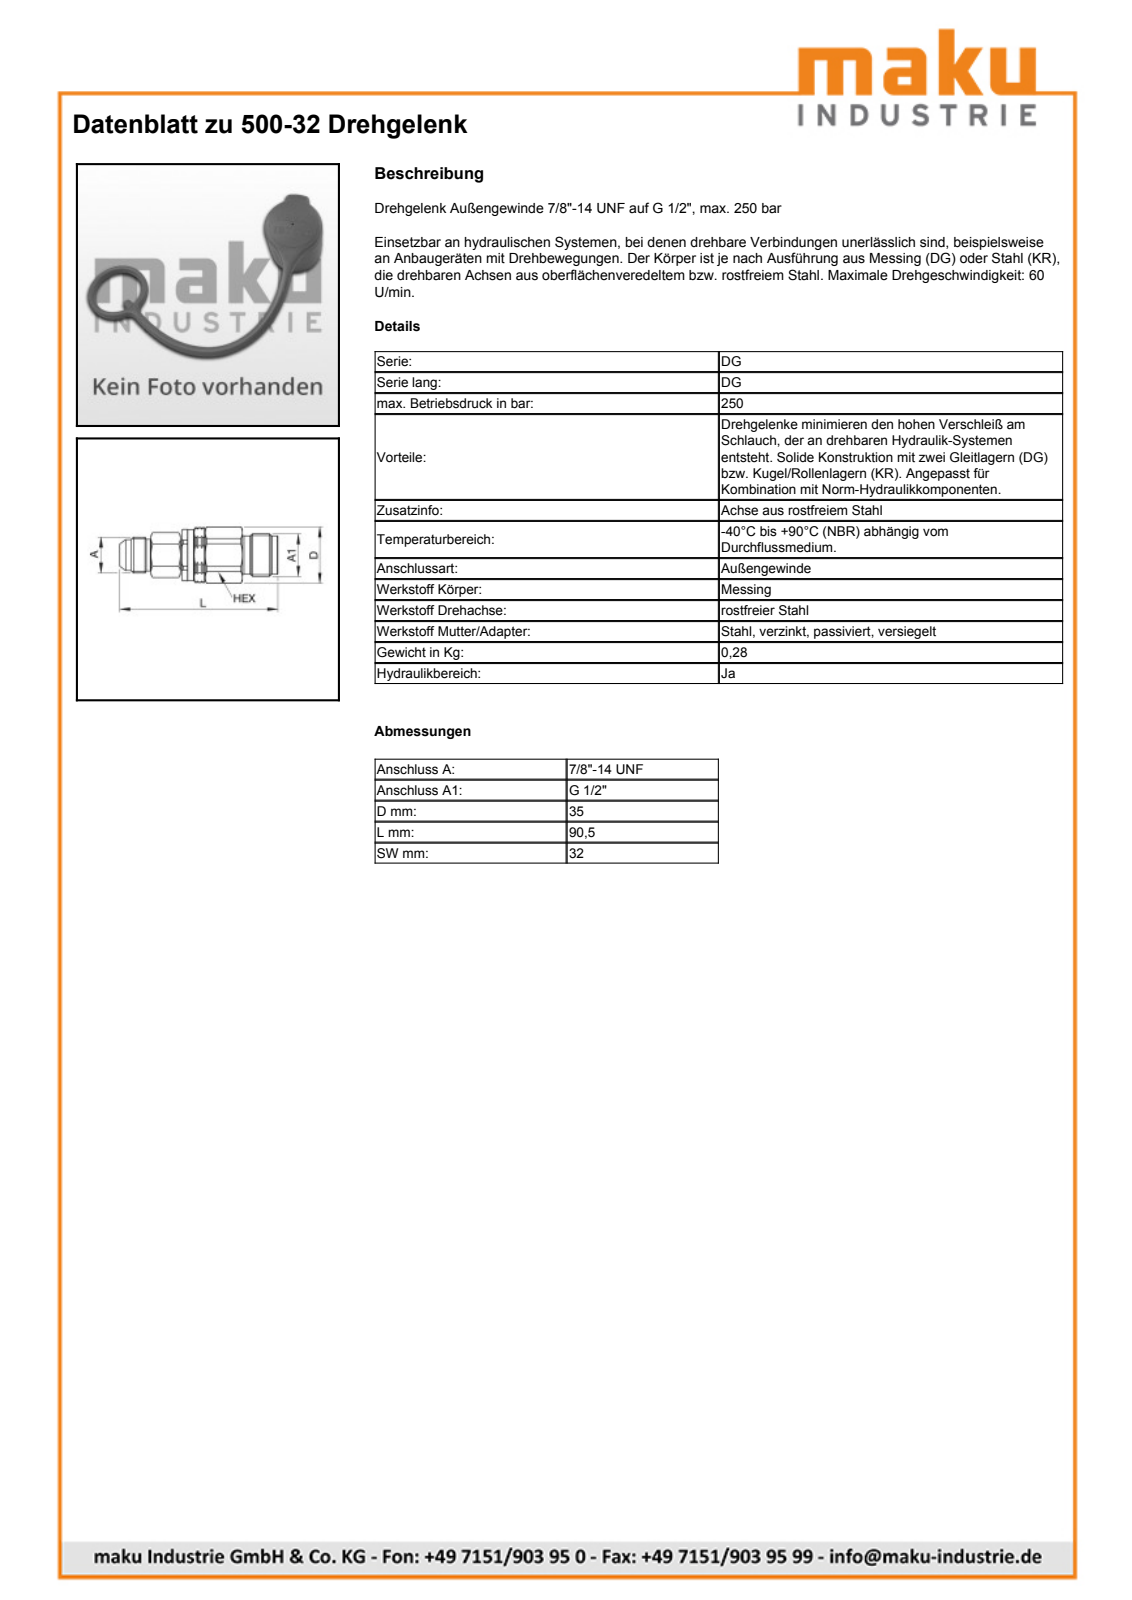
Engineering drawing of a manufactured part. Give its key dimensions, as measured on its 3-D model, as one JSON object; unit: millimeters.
{"part_name": "500-32", "step_written_by": "SolidWorks 2009 (AUTOMOTIVE_DESIGN)", "units": "millimeters", "bodies": {"solids": 1, "faces": 193, "planar": 73, "cylindrical": 52, "other": 68}, "overall_size": [90.47, 35, 32], "volume_mm3": 41519, "surface_area_mm2": 13820, "round_holes": [[11.8, 1], [12, 1], [13, 1], [16.79, 1], [18.4, 1], [30.2, 1]], "round_bosses_or_shafts": [[31.5, 1], [30, 1], [22.23, 1], [20.95, 1], [19.6, 1], [19.2, 1], [18, 1], [17.5, 1]], "partial_cylinders_radius": [[14.53, 1], [16, 1], [17, 1], [17.5, 1]], "face_to_face_distances": [4, 28, 32, 24, 38.05, 1.5, 2.5, 26.5, 30.5, 18.3]}
